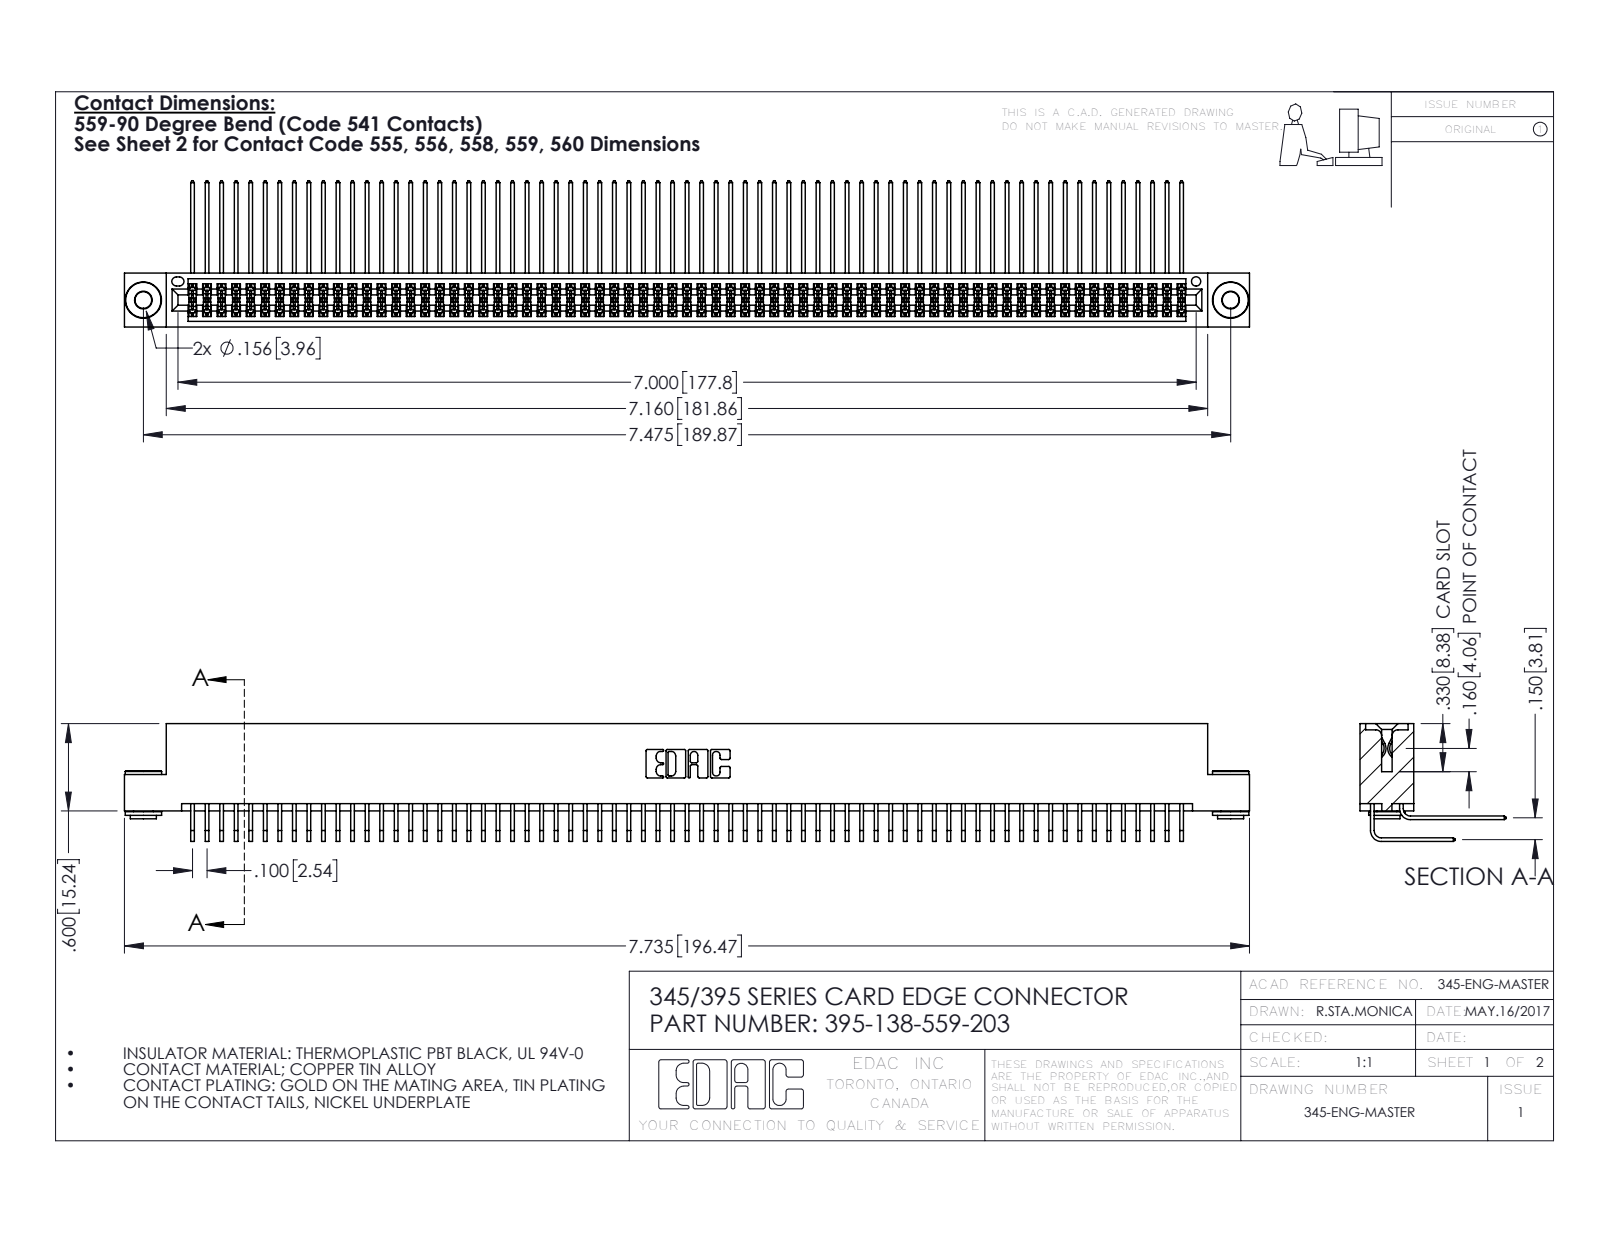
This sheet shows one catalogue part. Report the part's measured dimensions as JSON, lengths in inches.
{"part_name": "345 Part_Flush Mounting Lugs - 0.156 Dia-TH; 345-250-002_345-250-002-102; 395-138-559-203; 345-292-001_559 Tail - 2 (+1 more)", "step_written_by": "SolidWorks 2016 (CONFIG_CONTROL_DESIGN)", "units": "inches", "bodies": {"solids": 141, "faces": 7340, "planar": 4920, "cylindrical": 2412, "other": 8}, "overall_size": [7.735, 1.005, 0.809], "volume_in3": 1.23, "surface_area_in2": 53.1, "round_holes": [[0.116, 2], [0.156, 2], [0.064, 1]], "round_bosses_or_shafts": [[0.25, 2], [0.18, 2], [0.136, 2]], "partial_cylinders_radius": [[0.006, 275], [0.01, 22], [0.007, 6], [0.031, 6], [0.026, 3], [0.014, 2], [0.019, 2], [0.022, 2]], "face_to_face_distances": [0.072, 0.298, 0.2, 0.37, 0.025, 0.098, 0.272, 0.225, 0.175, 0.15], "hole_center_spacings": [0.27, 7.239, 7.475]}
